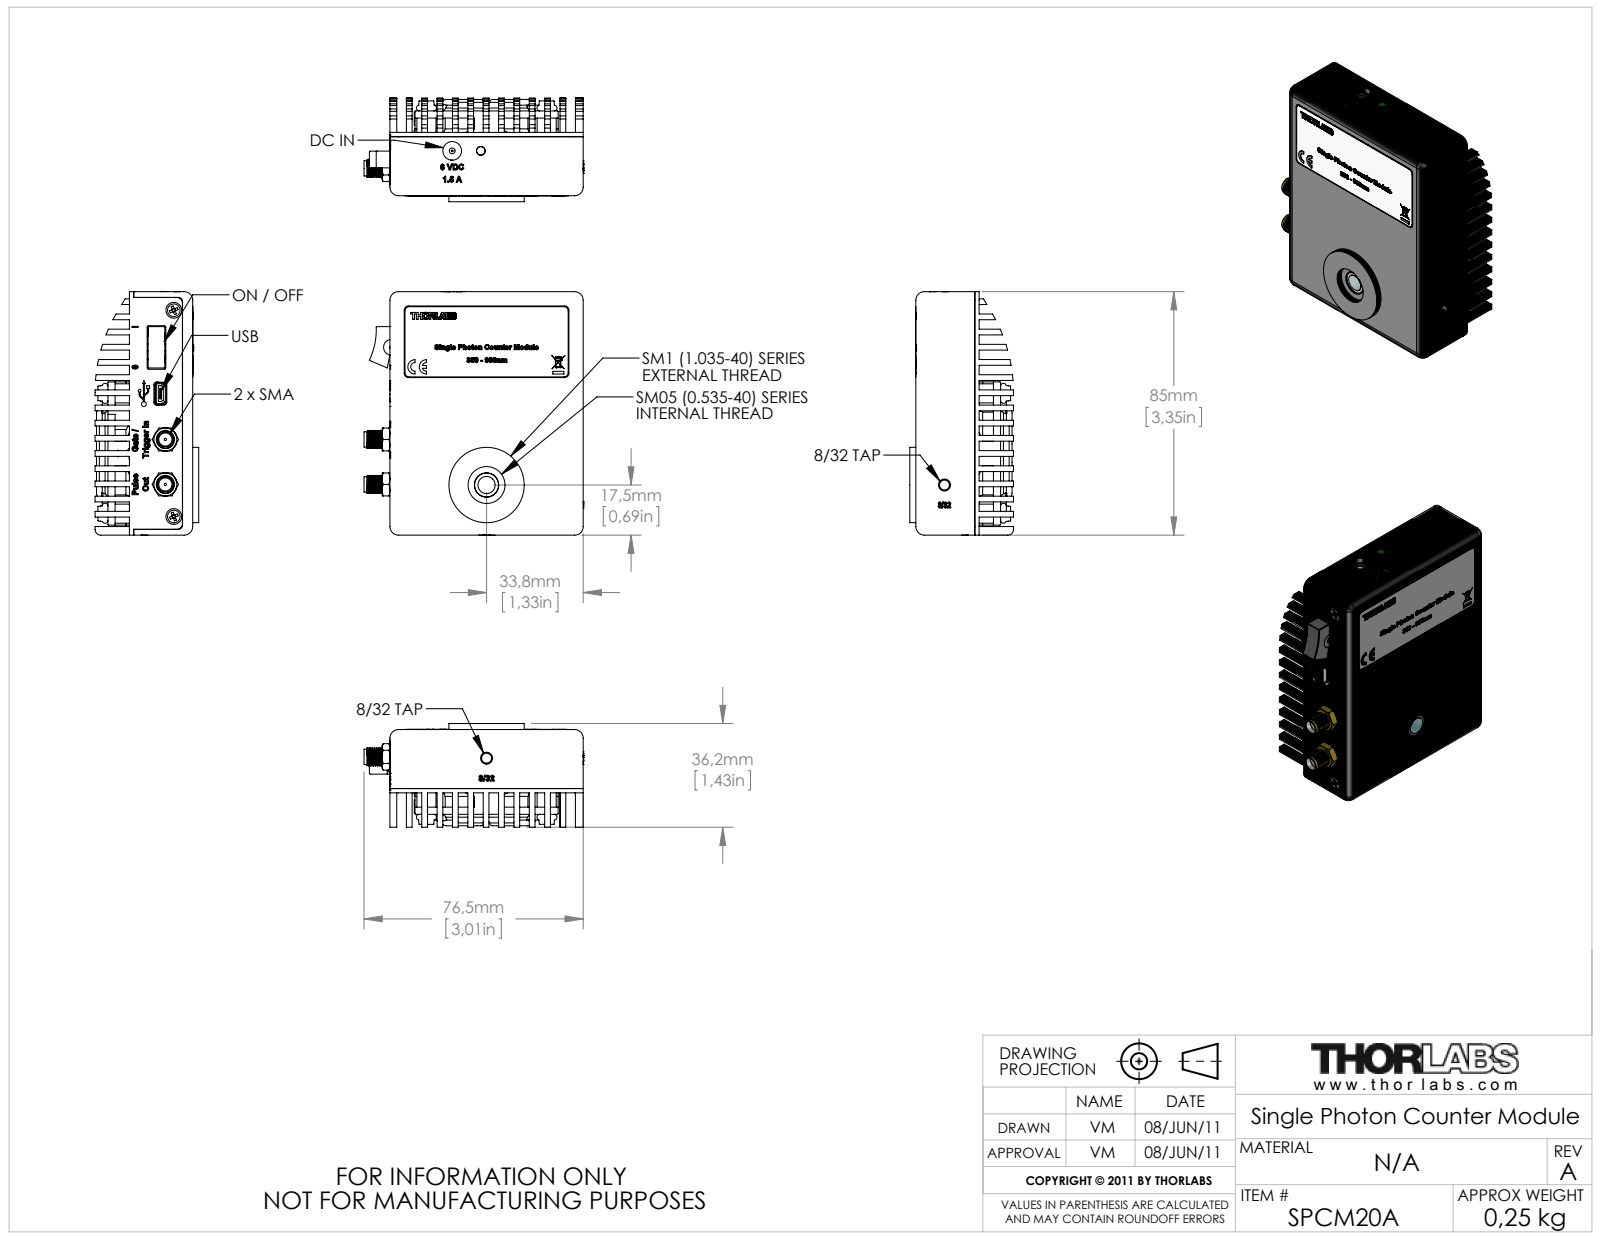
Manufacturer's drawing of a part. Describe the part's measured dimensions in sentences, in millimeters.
The part is named "SCPM rev B var2". Its 3-D file was written by "SolidWorks 2011 (CONFIG_CONTROL_DESIGN)". It is 0 solids with 4298 faces: 2831 planar, 552 cylindrical and 915 other. Overall it measures 85 by 76.54 by 36.2 millimeters. Round holes: 13 of diameter 1.6, 7 of diameter 2, 7 of diameter 2.4, 4 of diameter 2.2, 4 of diameter 2.9, 4 of diameter 3.7, 3 of diameter 1.02, 2 of diameter 0.8, 2 of diameter 2.6, 2 of diameter 3.45, 2 of diameter 4.17, 2 of diameter 4.2. Round bosses or shafts: 10 of diameter 3, 8 of diameter 2, 6 of diameter 5.5, 4 of diameter 6.66, 3 of diameter 0.45, 2 of diameter 5.35, 2 of diameter 0.76, 1 of diameter 26.29. Partial cylindrical surfaces (rounded edges, fillets, slot ends): 39 of radius 3, 33 of radius 0.25, 15 of radius 1, 14 of radius 1.5, 12 of radius 0.5, 6 of radius 0.3, 6 of radius 0.7, 5 of radius 2. The main face-to-face distances are 1.5, 3, 6.45, 1.55, 2, 4.55, 4.95, 14.5, 13.95, 5. The hole center spacings are 29.7, 42, 1.27, 29.98, 46.33, 1.8, 9.42, 10.14.
